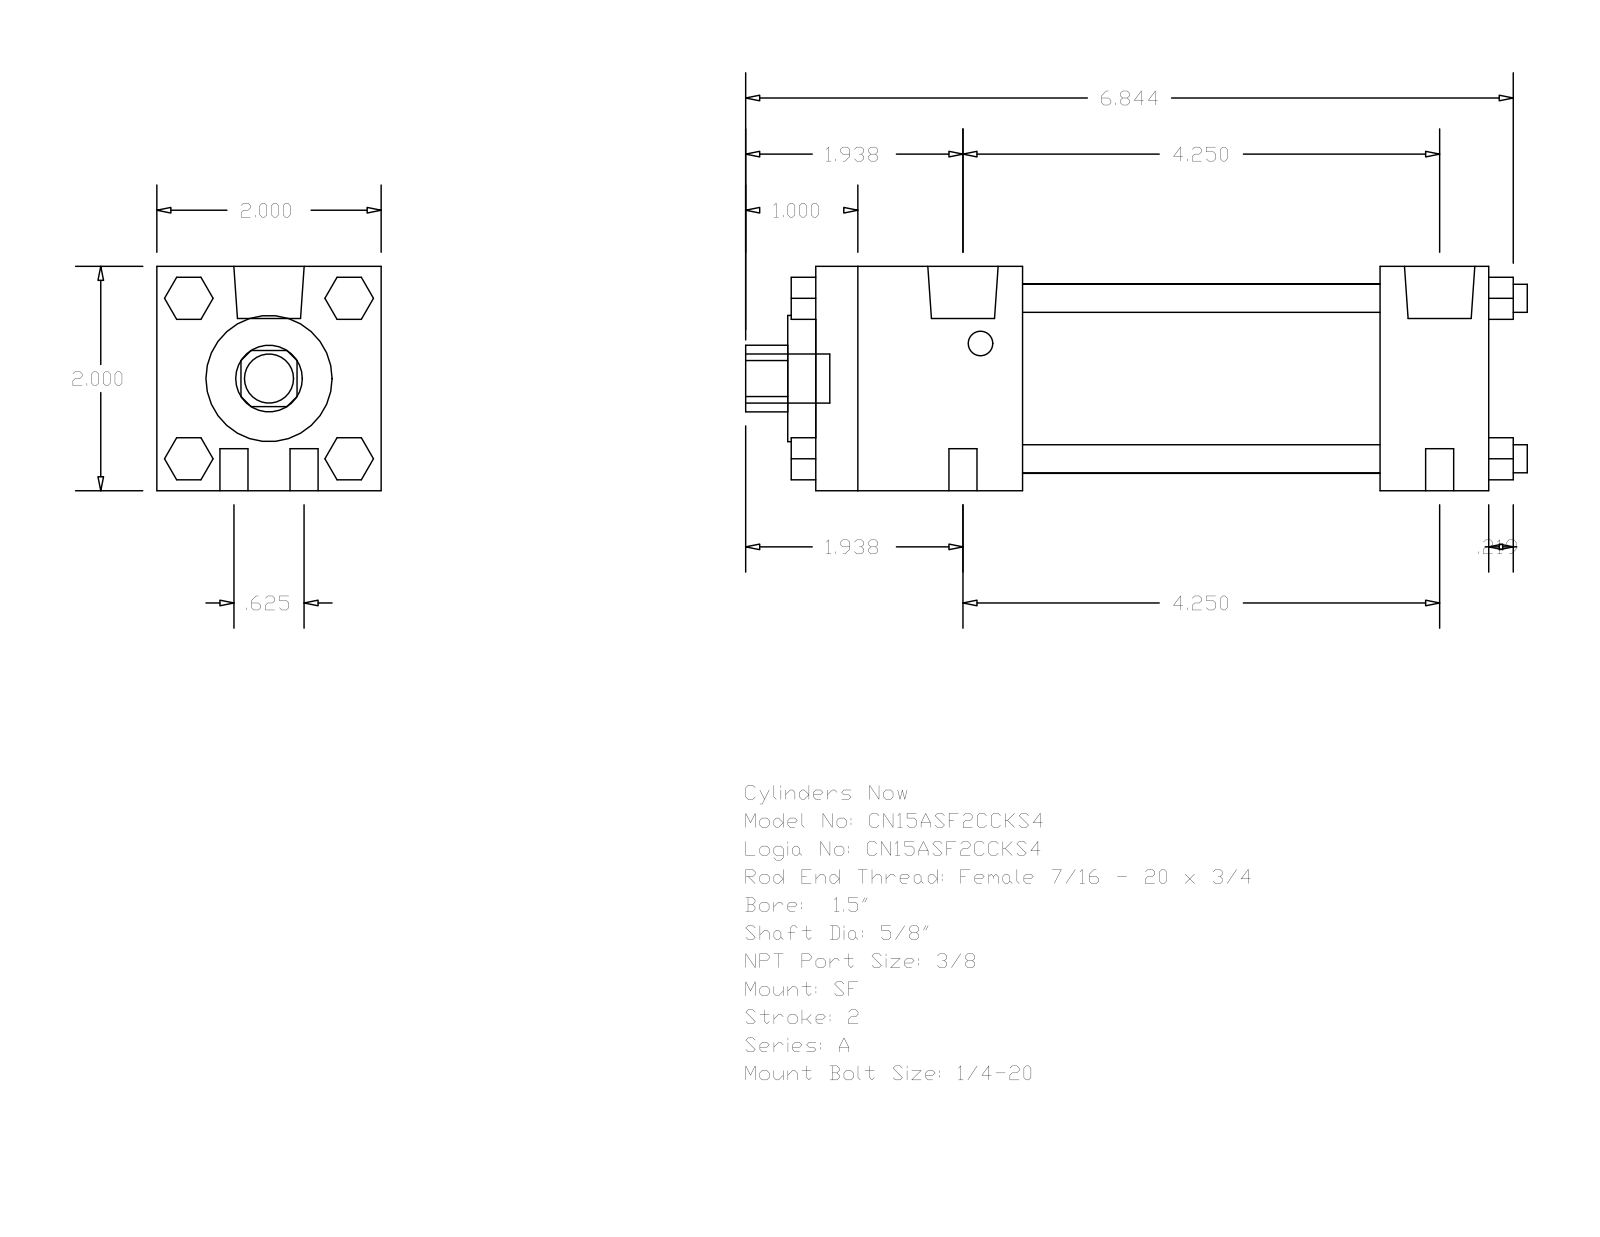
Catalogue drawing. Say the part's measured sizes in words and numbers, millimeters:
The part is named "A_SF__0150_0.625". Its 3-D file was written by "GSSL Pune (CONFIG_CONTROL_DESIGN)". It is 0 solids with 124 faces: 94 planar, 30 cylindrical and 0 other. Overall it measures 177.01 by 50.8 by 50.8 millimeters. Round holes: 1 of diameter 15.88, 1 of diameter 28.57, 1 of diameter 42.93. Round bosses or shafts: 8 of diameter 6.35, 2 of diameter 15.93, 2 of diameter 5.56, 1 of diameter 11.11. Partial cylindrical surfaces (rounded edges, fillets, slot ends): 1 of radius 7.54. The main face-to-face distances are 50.8, 152.4, 46.83, 127.79, 80.96, 105.57, 24.61, 9.52, 6.35, 53.18.
